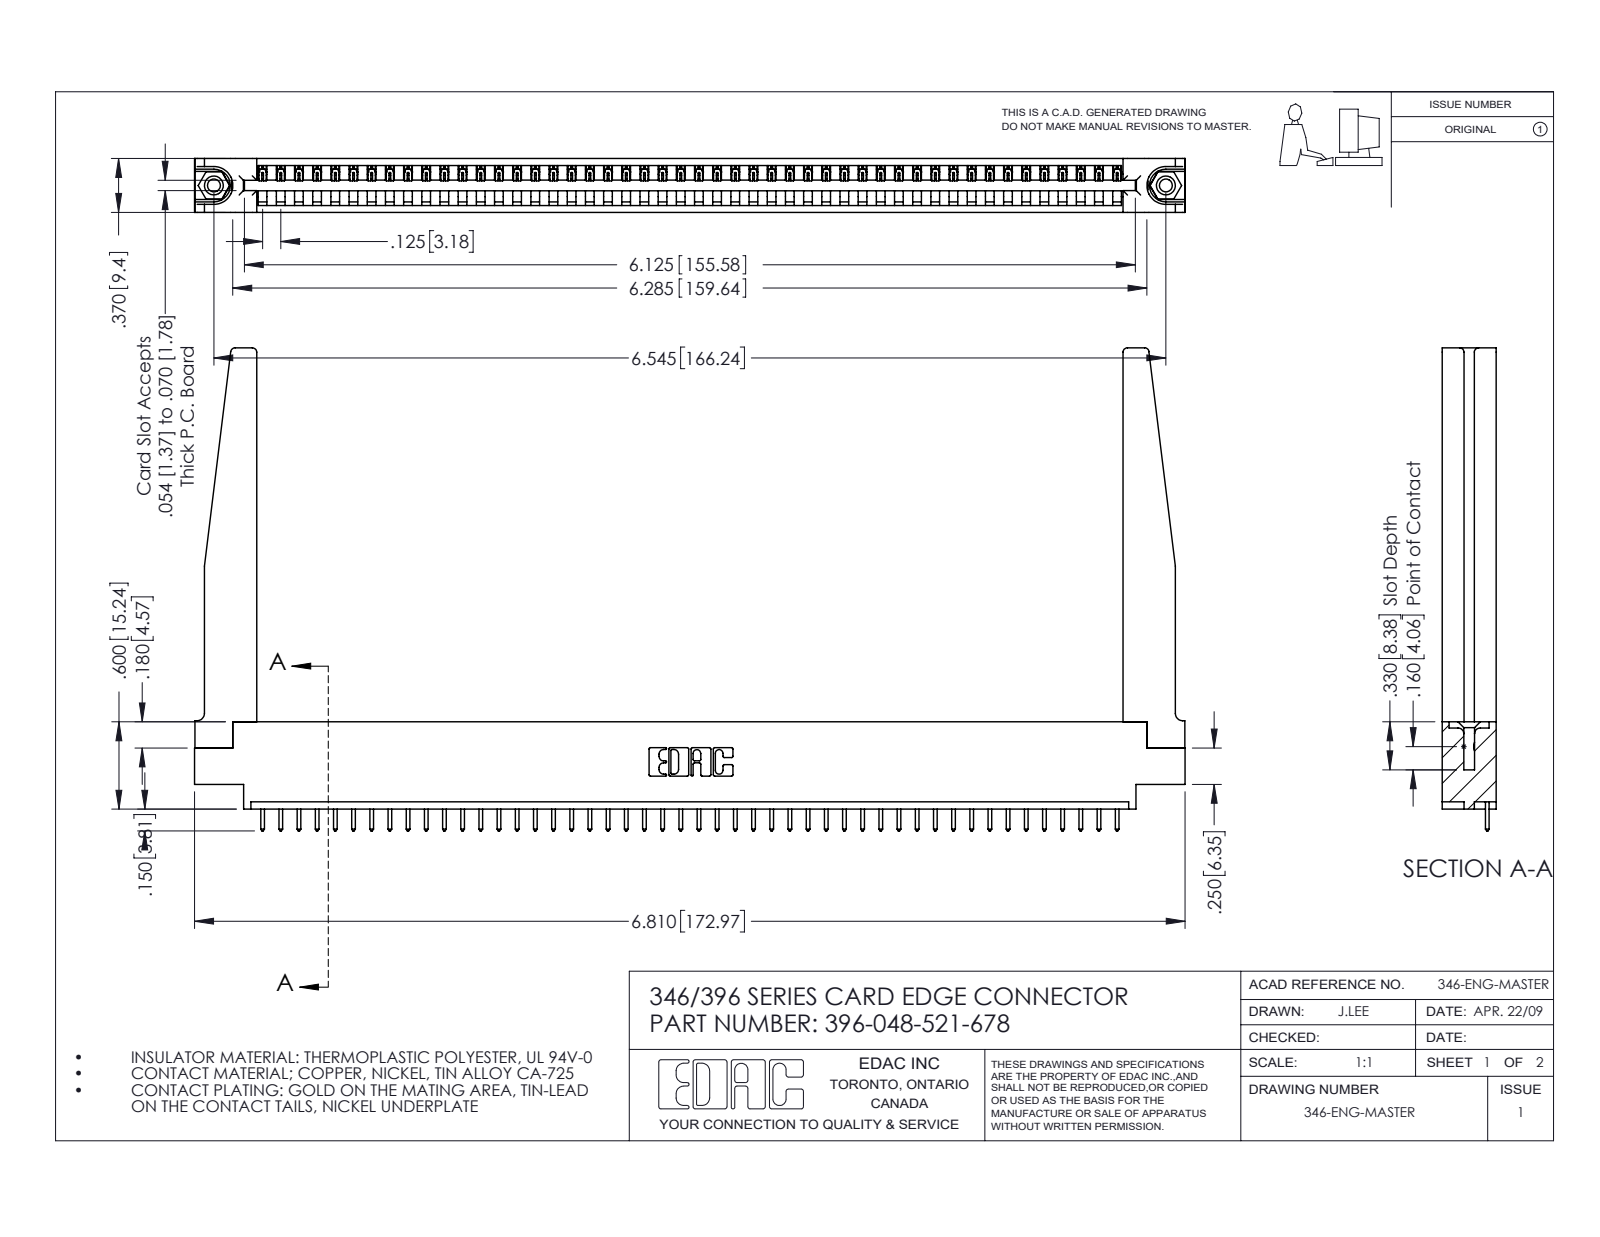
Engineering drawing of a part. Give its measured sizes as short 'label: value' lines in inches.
name: 346 Part_0.170 Offset - 0.156 Dia-TH; 396-048-521-678; 345-250-001_345-250-001-102; 345-292-001_345-293-121 (+1 more)
written by: SolidWorks 2016 (CONFIG_CONTROL_DESIGN)
unit: in
bodies: 53 solids, 3144 faces (2142 planar, 950 cylindrical, 52 other)
size: 6.81 × 3.32 × 0.37
volume: 1.417 in³; area: 41.24 in²
holes: 2× ⌀0.089, 2× ⌀0.125, 2× ⌀0.156, 1× ⌀0.064
bosses: 2× ⌀0.155
rounds: 96× R0.006, 96× R0.01, 22× R0.01, 8× R0.03, 6× R0.007, 6× R0.031, 3× R0.026, 2× R0.031
face distances: 0.37, 0.048, 0.322, 0.072, 0.148, 0.15, 0.25, 0.298, 0.025, 0.222
hole spacings: 0.246, 6.336, 6.545
